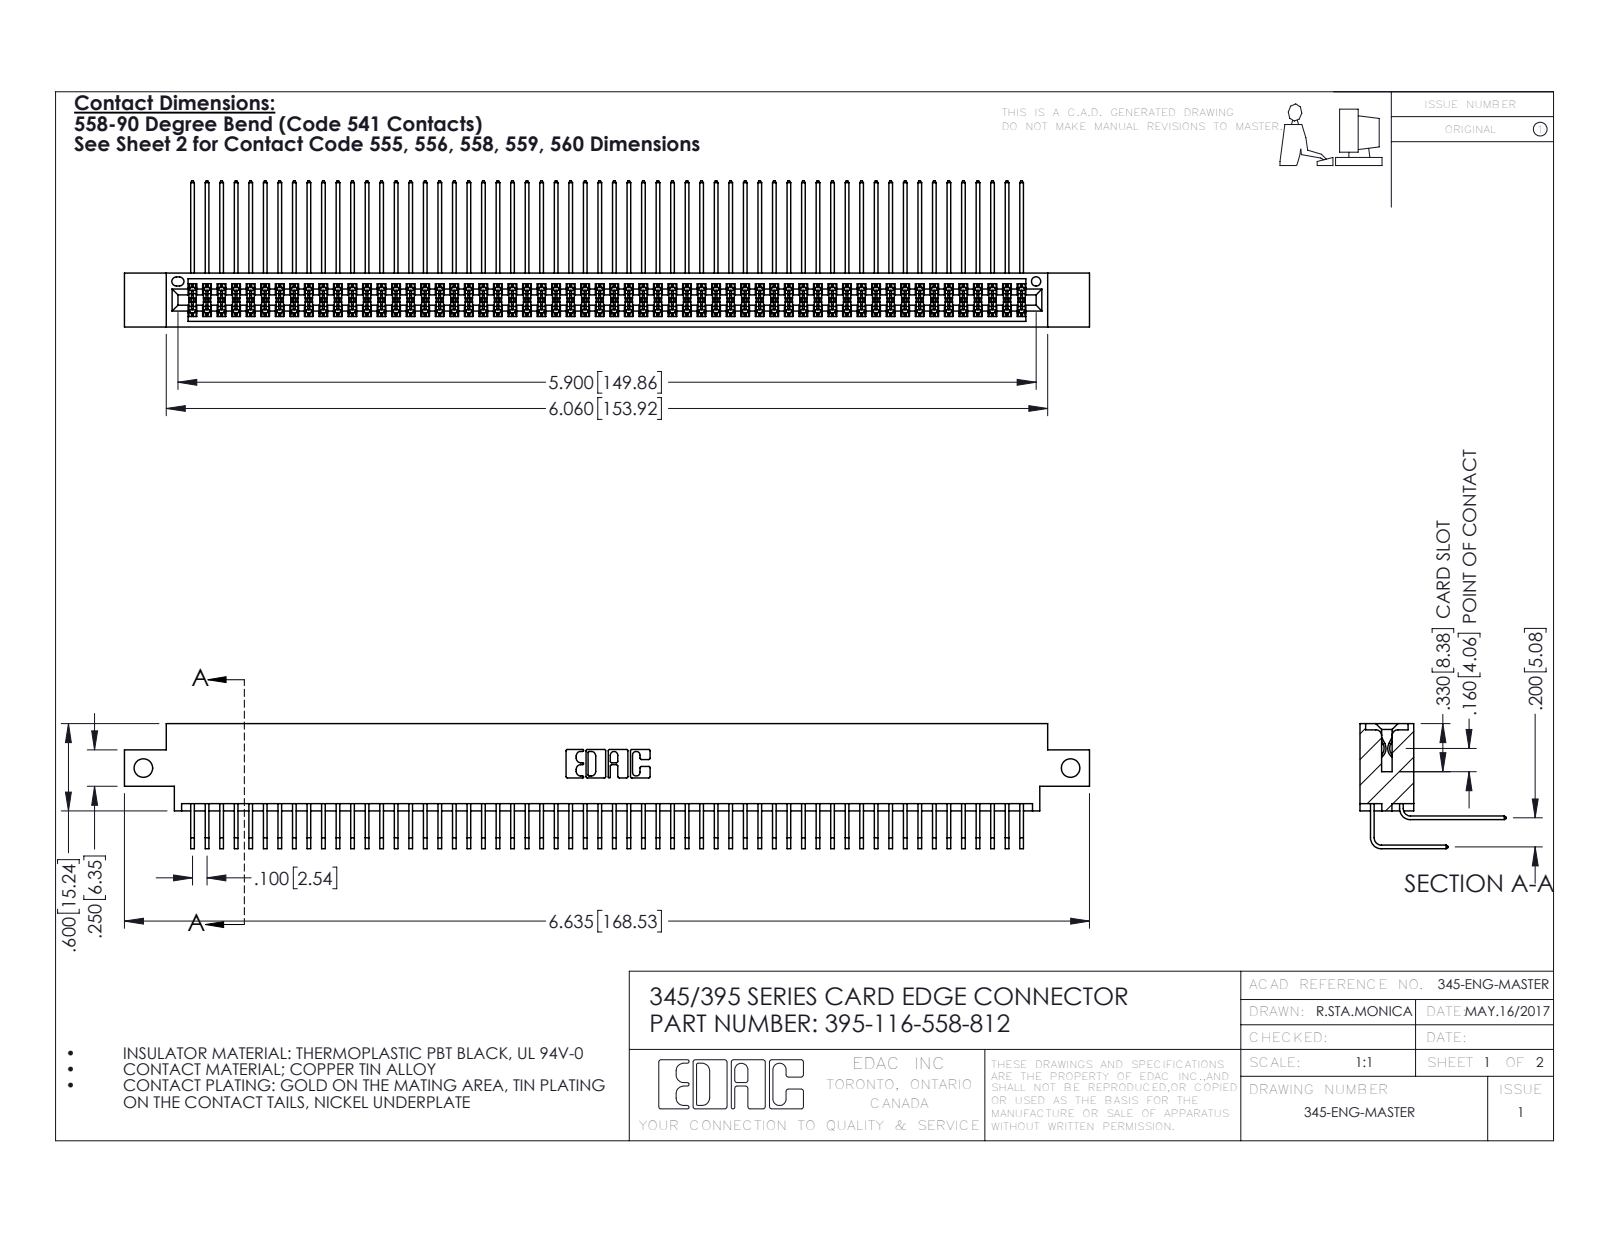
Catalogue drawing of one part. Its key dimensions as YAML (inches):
part_name: "345-292-001_558 559 Tail - 1; 395-116-558-812; 345 Part_0.170 Offset - Side Mount; 345-292-001_558 Tail - 2"
step_written_by: "SolidWorks 2016 (CONFIG_CONTROL_DESIGN)"
units: inches
bodies: {solids: 117, faces: 6162, planar: 4144, cylindrical: 2018, other: 0}
overall_size: [6.635, 1.005, 0.859]
volume: 1.037
surface_area: 44.29
round_holes:
  - {diameter: 0.128, count: 2}
  - {diameter: 0.064, count: 1}
partial_cylinders:
  - {radius: 0.006, count: 174}
  - {radius: 0.01, count: 22}
  - {radius: 0.007, count: 6}
  - {radius: 0.031, count: 6}
  - {radius: 0.026, count: 3}
  - {radius: 0.014, count: 2}
  - {radius: 0.019, count: 2}
  - {radius: 0.022, count: 2}
face_to_face_distances: [0.072, 0.298, 0.2, 0.37, 0.098, 0.272, 0.025, 0.225, 0.175, 0.025]
hole_center_spacings: [6.375]
